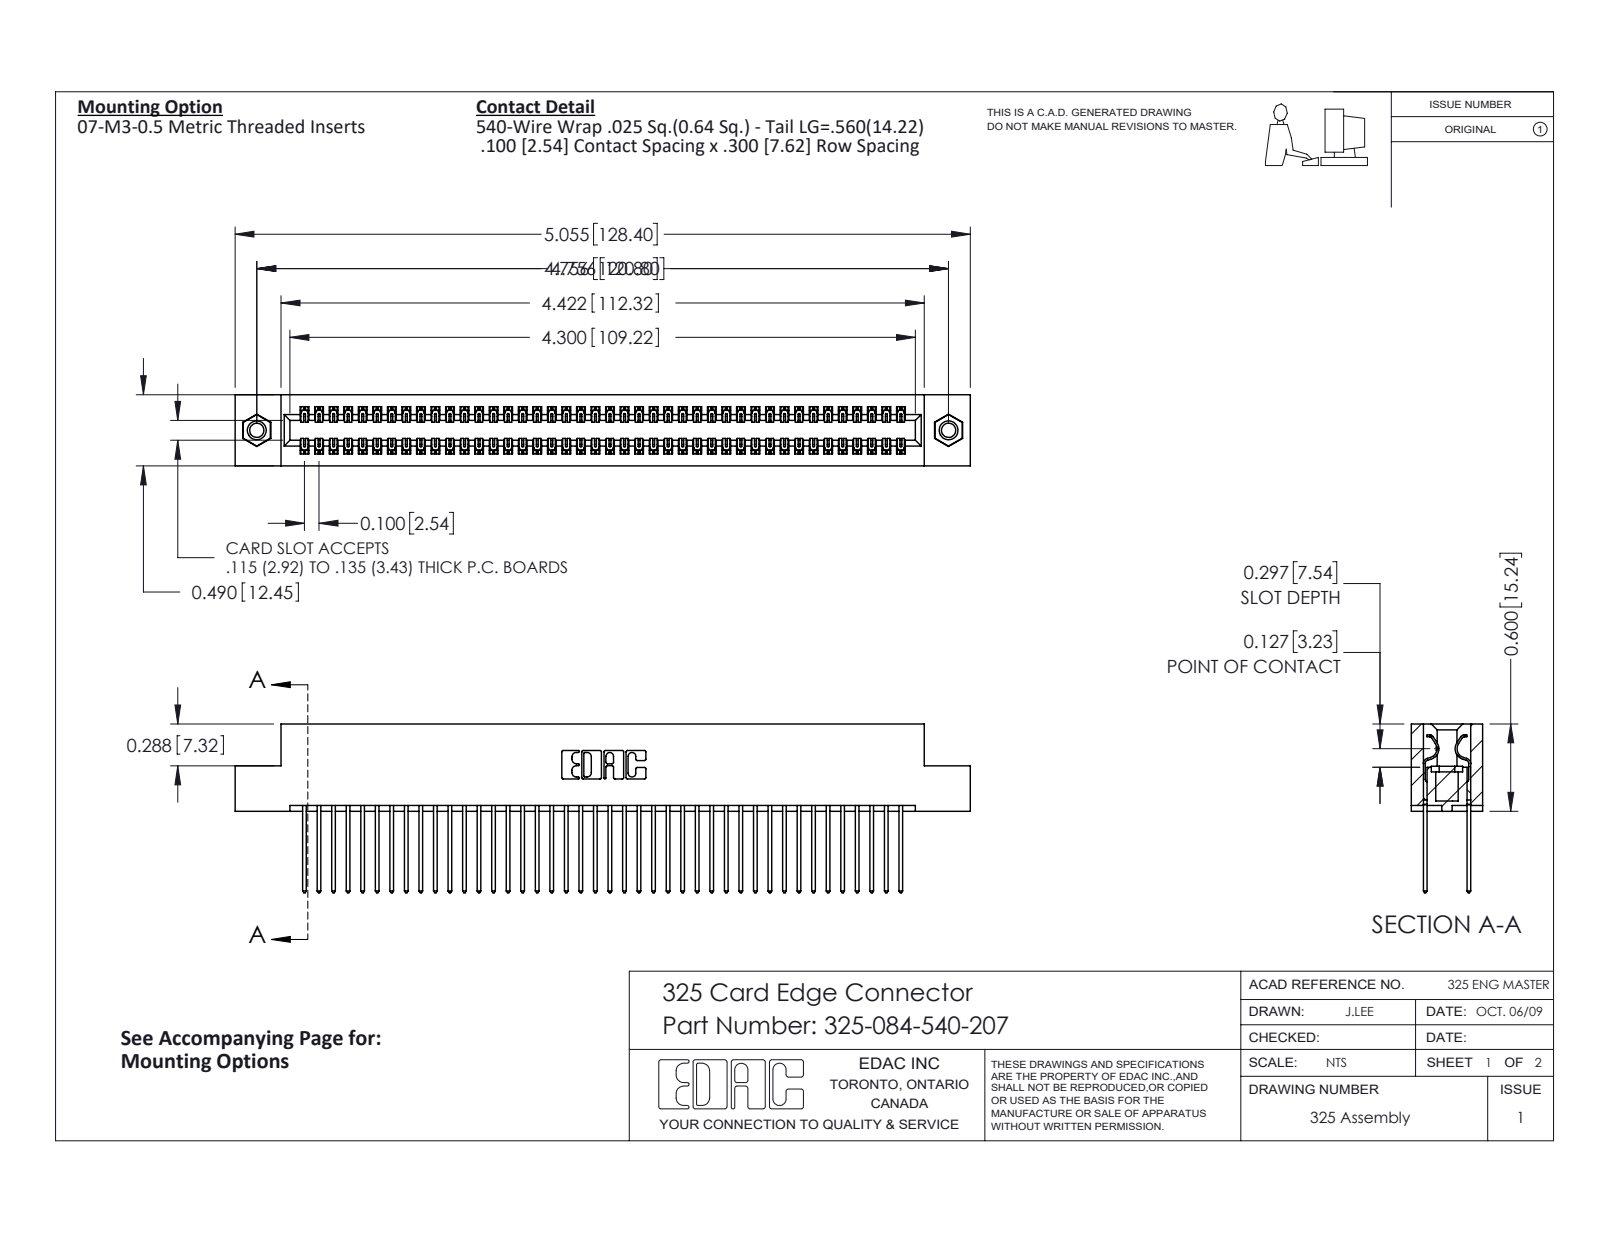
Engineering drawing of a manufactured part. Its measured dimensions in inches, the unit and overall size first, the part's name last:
Units: inches
Overall size (bounding box): 5.055 × 1.16 × 0.49
Round holes (diameter × count): ⌀0.098 ×2, ⌀0.125 ×2, ⌀0.16 ×2
Round bosses / shafts (diameter × count): ⌀0.155 ×2
Partial cylindrical surfaces — rounded edges, fillets, slot ends (radius × count): R0.006 ×126, R0.01 ×84, R0.01 ×22, R0.007 ×6, R0.031 ×6, R0.026 ×3, R0.014 ×2, R0.022 ×2
Main face-to-face distances: 0.083, 0.407, 0.3, 0.107, 0.383, 0.025, 0.49, 0.325, 0.275, 0.56
Hole centre spacings: 4.756
Volume: 1.03 in³ · Surface area: 34.06 in²
Bodies: 87 solids, 4542 faces (3126 planar, 1400 cylindrical, 16 other)
Part name (STEP PRODUCT): 345-250-001_345-250-005-103; 325-292-001_325-293-140; 325-084-540-207; 325 Part_TI
STEP written by: SolidWorks 2016 (CONFIG_CONTROL_DESIGN)
